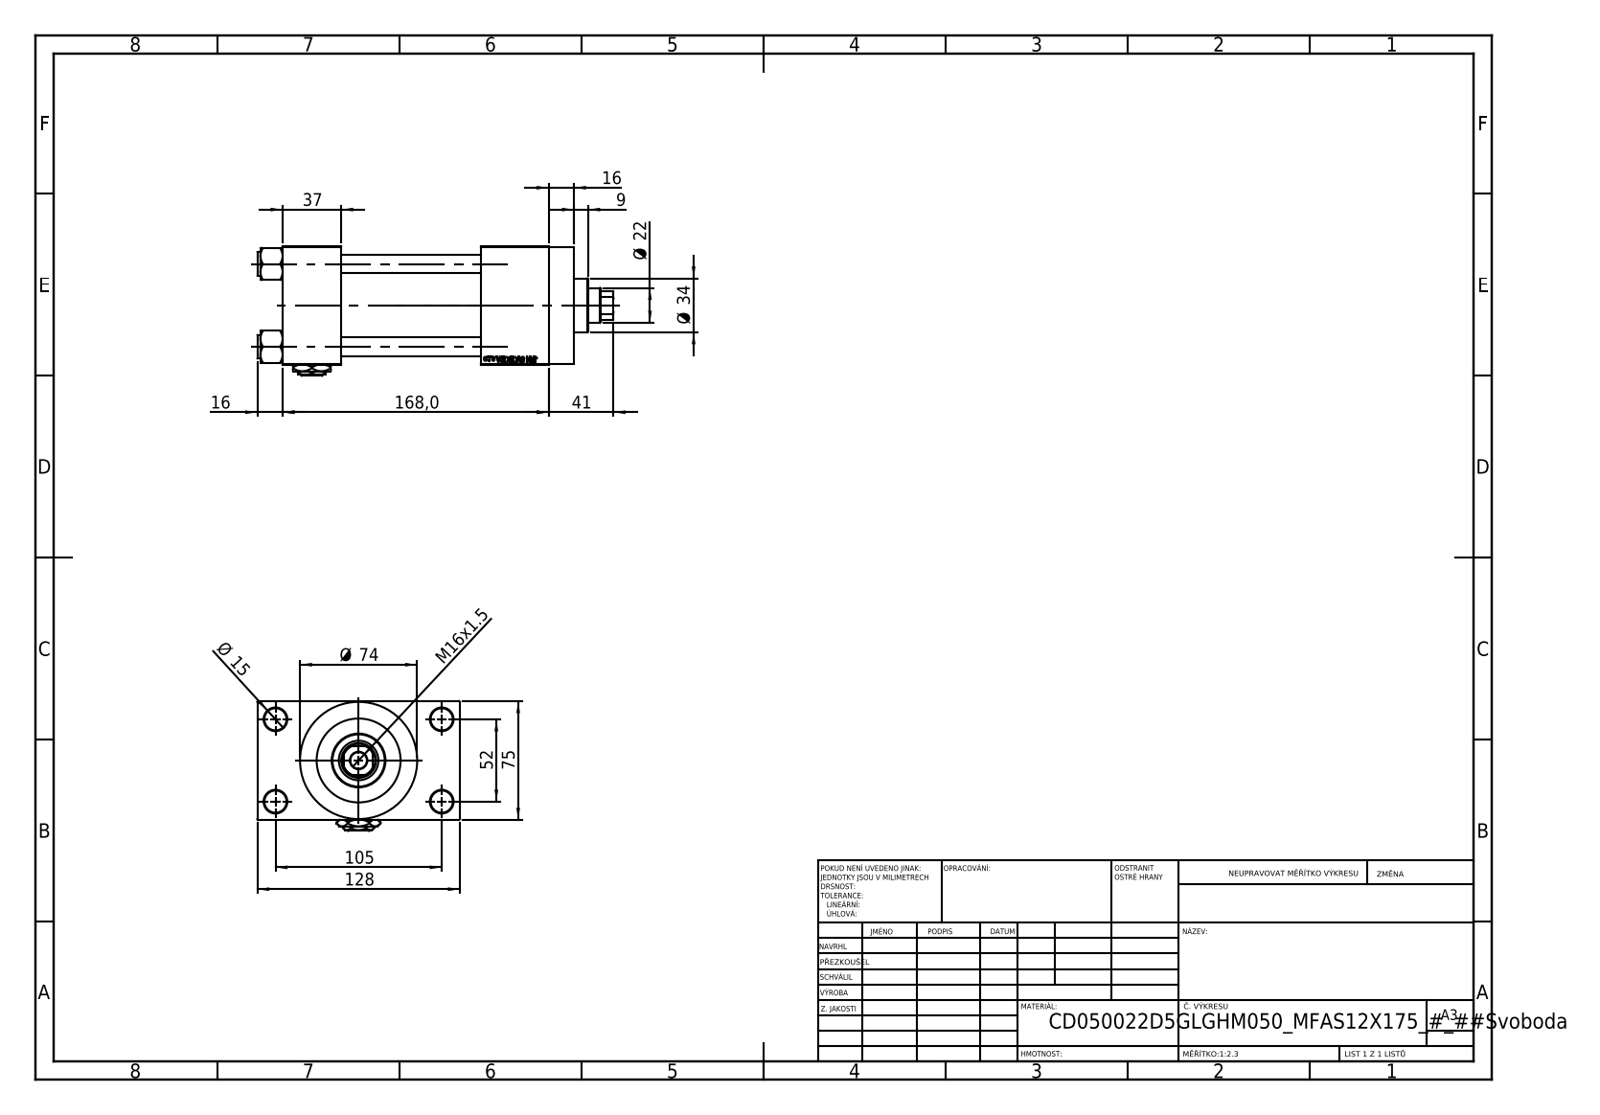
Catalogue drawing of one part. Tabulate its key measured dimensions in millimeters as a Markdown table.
| quantity | value |
| --- | --- |
| part name | V215CD_NUT_M5_D; Zatka_pro_OIL_PORT; V215CD_VCP_D; V215CD_VC_A (+2 more) |
| STEP written by | SolidWorks 2019 (CONFIG_CONTROL_DESIGN) |
| units | millimeters |
| bodies | 12 solids, 1146 faces (519 planar, 89 cylindrical, 538 other) |
| overall size | 225 × 128 × 82 |
| volume | 849 267 mm³ |
| surface area | 182 994 mm² |
| round holes (diameter × count) | 12 × 4, 14 × 4, 7 × 2, 20.96 × 2, 30 × 2, 10.5 × 1, 22 × 1, 25 × 1, 41 × 1, 50 × 1, 53 × 1 |
| round bosses / shafts (diameter × count) | 15 × 4, 74 × 1, 56 × 1, 34 × 1 |
| partial cylindrical surfaces (radius × count) | 10.5 × 1 |
| main face-to-face distances | 75, 88, 37, 125, 26.5, 101.5, 43, 168, 131, 16 |
| hole center spacings | 26.35, 36.98, 52.3, 58.43, 58.59, 78.65, 94.37, 52 |
